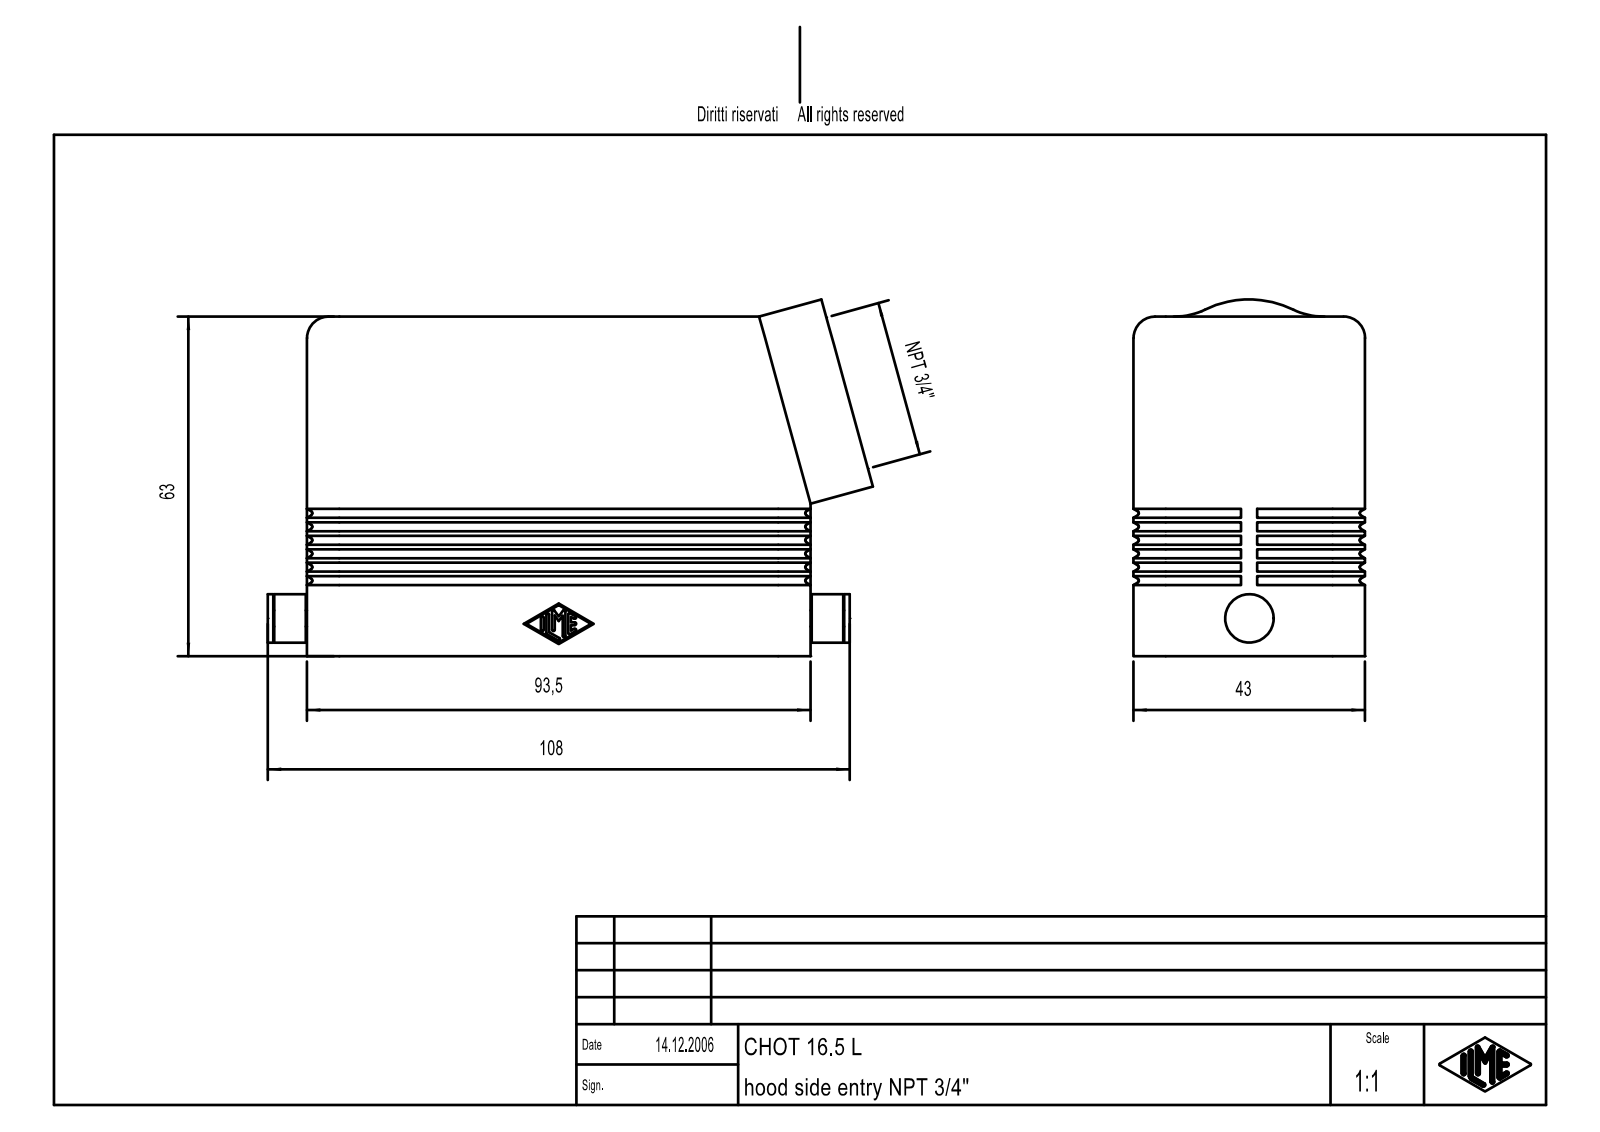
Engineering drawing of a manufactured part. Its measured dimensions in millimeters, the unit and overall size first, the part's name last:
Units: millimetres
Overall size (bounding box): 112.32 × 66.18 × 43
Round holes (diameter × count): ⌀2.46 ×4, ⌀3.1 ×4
Round bosses / shafts (diameter × count): ⌀9 ×1, ⌀3 ×1
Partial cylindrical surfaces — rounded edges, fillets, slot ends (radius × count): R0.4 ×48, R0.25 ×14, R1.5 ×4, R3 ×4, R5 ×4, R6 ×4, R4 ×3, R10.75 ×1
Main face-to-face distances: 3, 40, 37, 43, 4.33, 8.25, 79.25, 82.25, 11.25, 90.5
Hole centre spacings: 27, 77.5, 82.07
Volume: 76 755 mm³ · Surface area: 42 288 mm²
Bodies: 1 solid, 518 faces (219 planar, 183 cylindrical, 116 other)
Part name (STEP PRODUCT): MSBO9921
STEP written by: Creo Elements/Direct Modeling 18.0B 02-Dec-2011 (C) Parametric Technology GmbH (AUTOMOTIVE_DESIGN)
